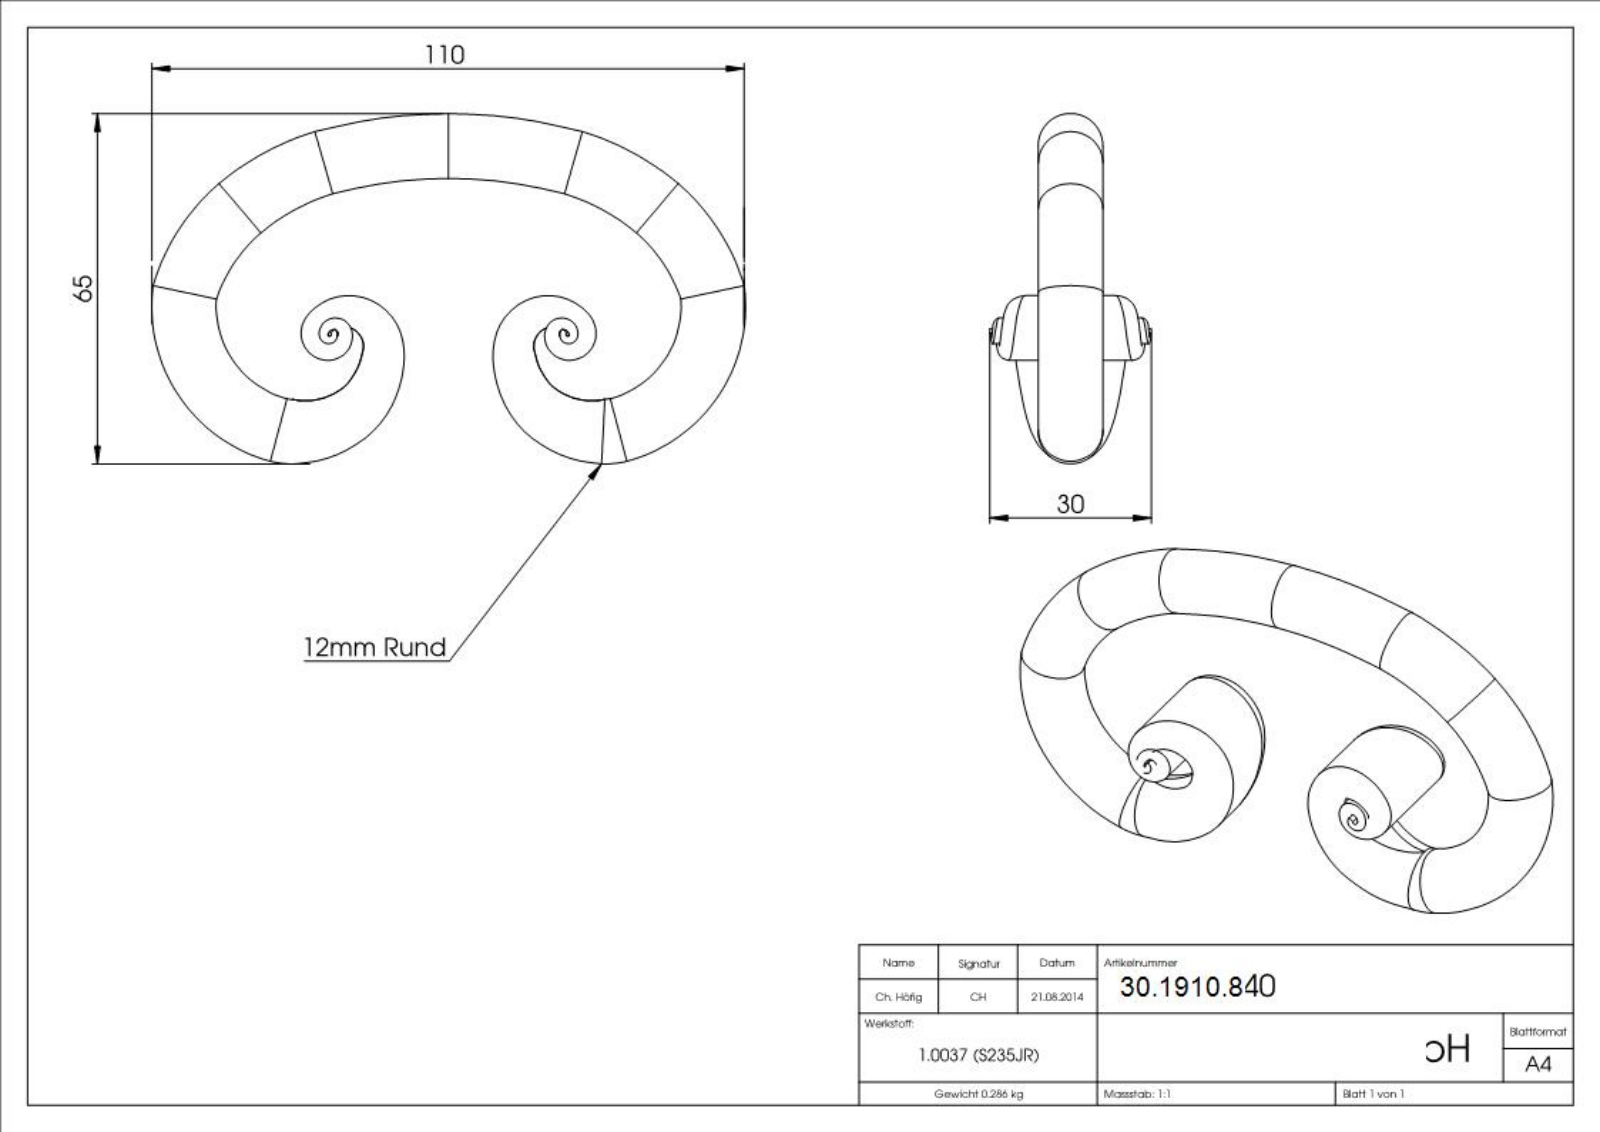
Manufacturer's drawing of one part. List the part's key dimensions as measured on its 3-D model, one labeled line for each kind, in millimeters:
Part name (STEP PRODUCT): 5640
STEP written by: SolidWorks 2015 (CONFIG_CONTROL_DESIGN)
Units: millimetres
Bodies: 1 solid, 143 faces (64 planar, 0 cylindrical, 79 other)
Overall size (bounding box): 110.29 × 65.01 × 30
Volume: 36 794 mm³ · Surface area: 14 037 mm²
Main face-to-face distances: 0.75, 1.78, 0.67, 1.21, 0.82, 1.96, 2.02, 0.43, 0.99, 1.03
